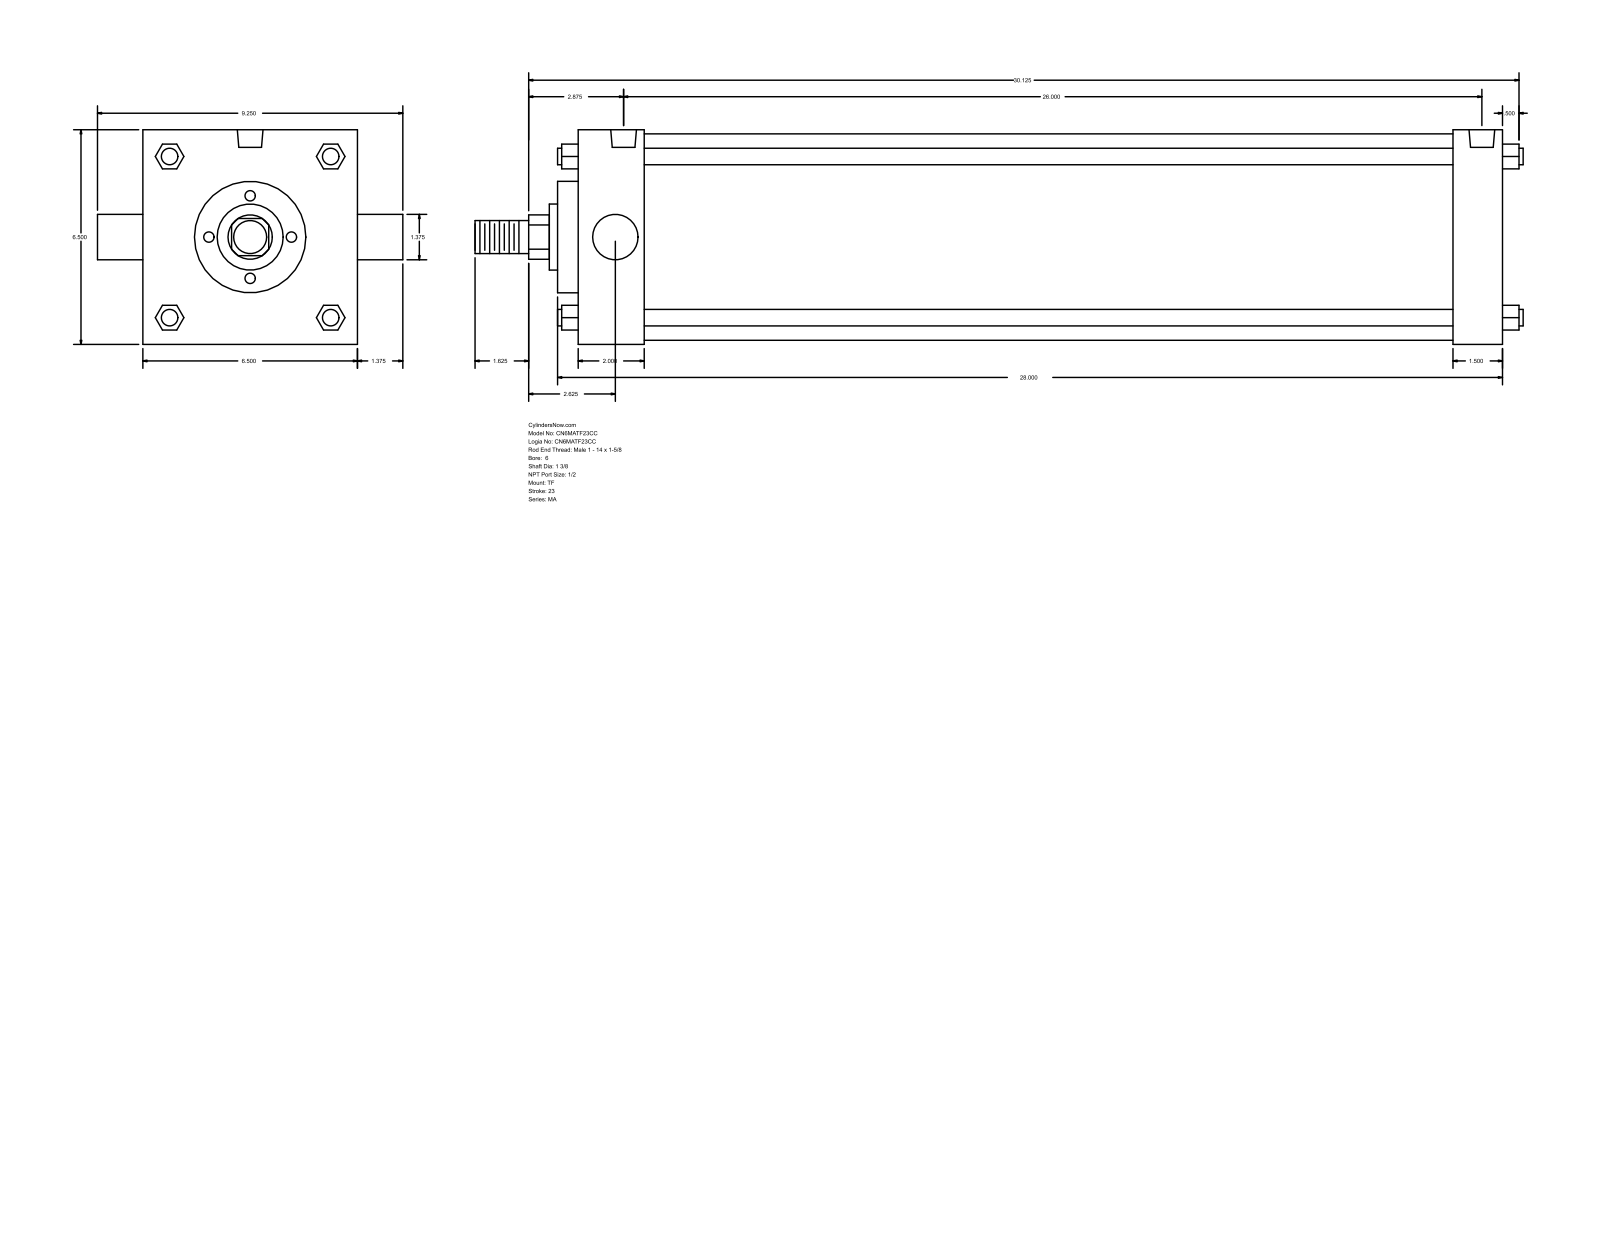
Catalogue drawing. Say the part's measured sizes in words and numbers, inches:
The part is named "MA_TF__0600_1.375". Its 3-D file was written by "GSSL Pune (CONFIG_CONTROL_DESIGN)". It is 0 solids with 122 faces: 93 planar, 29 cylindrical and 0 other. Overall it measures 31.75 by 9.25 by 6.5 inches. Round holes: 3 of diameter 0.687, 2 of diameter 0.778. Round bosses or shafts: 4 of diameter 0.5, 2 of diameter 1.375, 1 of diameter 6.25, 1 of diameter 3.375, 1 of diameter 2, 1 of diameter 1. Partial cylindrical surfaces (rounded edges, fillets, slot ends): 1 of radius 0.672. The main face-to-face distances are 6.5, 28.125, 1.5, 2, 26.125, 26.625, 24.625, 2.625, 0.625, 27.25. The hole center spacings are 0.125, 26, 26.125.
